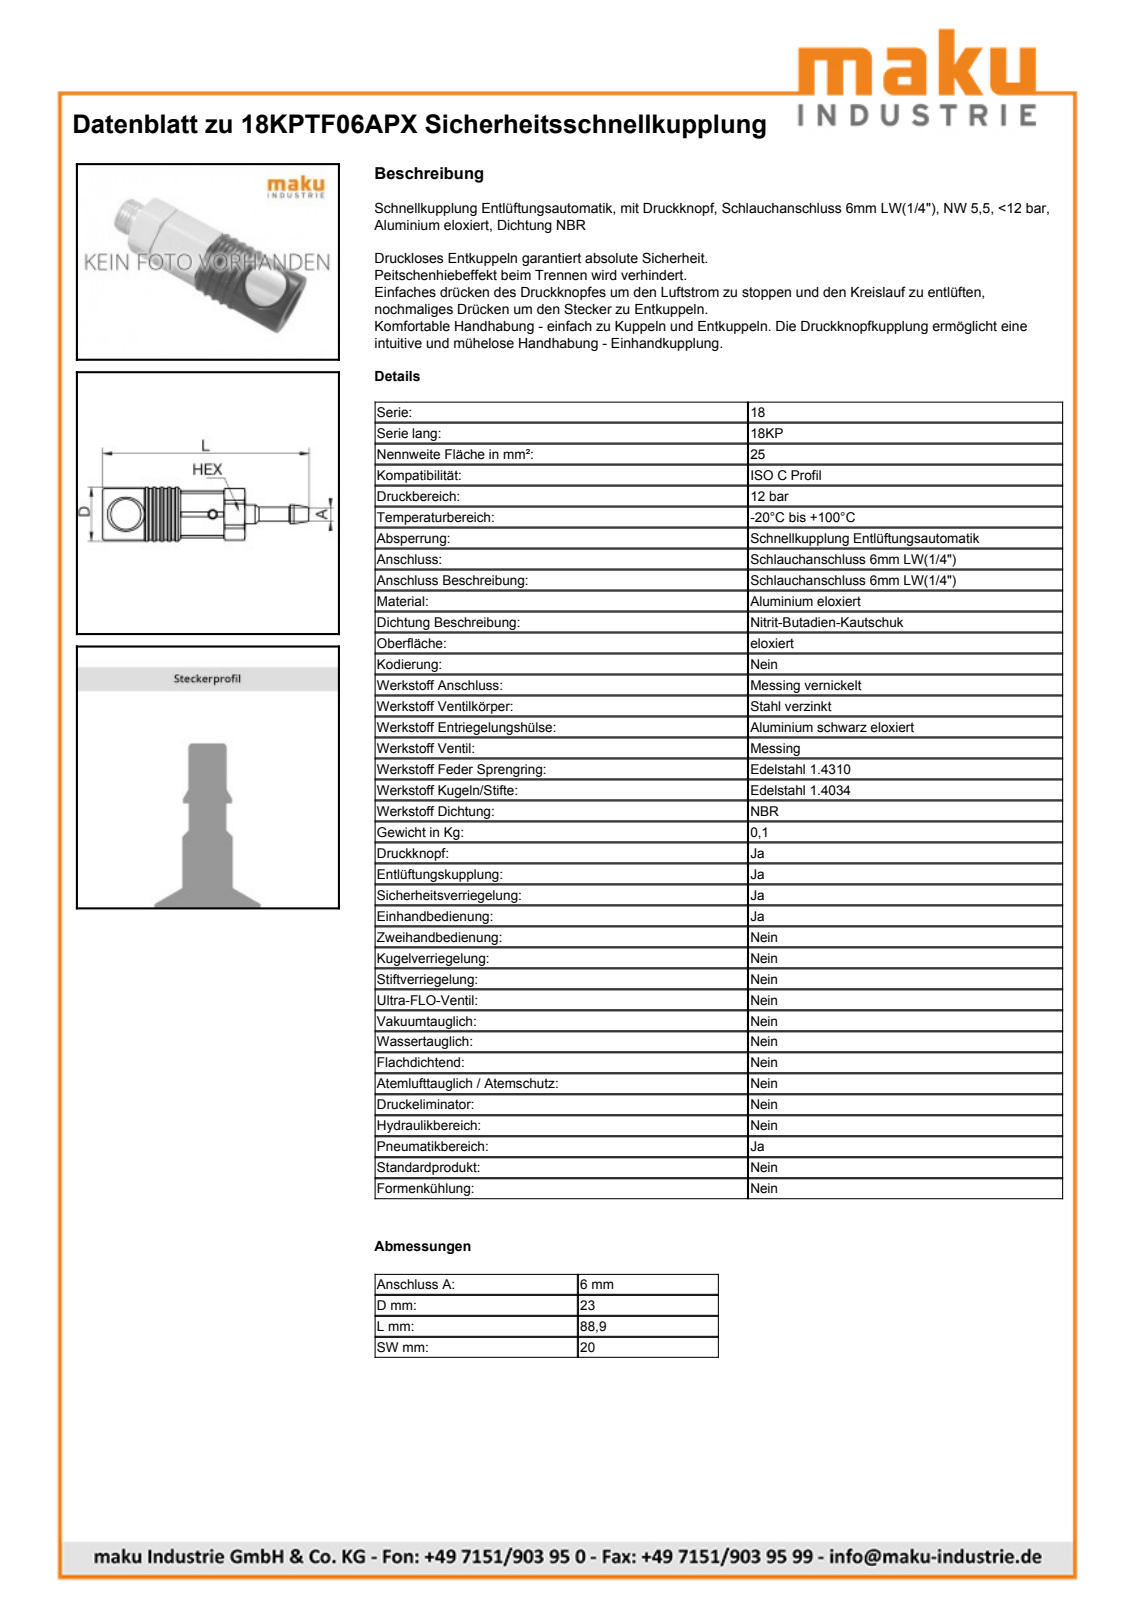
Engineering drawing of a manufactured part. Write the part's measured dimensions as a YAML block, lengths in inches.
part_name: "18KPTF06APX"
step_written_by: "Autodesk Inventor 2019 (CONFIG_CONTROL_DESIGN)"
units: inches
bodies: {solids: 27, faces: 300, planar: 95, cylindrical: 103, other: 102}
overall_size: [3.5, 0.906, 0.906]
volume: 1.88
surface_area: 30.55
round_holes:
  - {diameter: 0.098, count: 1}
  - {diameter: 0.138, count: 1}
  - {diameter: 0.157, count: 1}
  - {diameter: 0.217, count: 1}
  - {diameter: 0.276, count: 1}
  - {diameter: 0.335, count: 1}
  - {diameter: 0.398, count: 1}
  - {diameter: 0.409, count: 1}
  - {diameter: 0.413, count: 1}
  - {diameter: 0.437, count: 1}
  - {diameter: 0.508, count: 1}
  - {diameter: 0.553, count: 1}
round_bosses_or_shafts:
  - {diameter: 0.906, count: 1}
  - {diameter: 0.866, count: 1}
  - {diameter: 0.787, count: 1}
  - {diameter: 0.728, count: 1}
  - {diameter: 0.717, count: 1}
  - {diameter: 0.709, count: 1}
  - {diameter: 0.69, count: 1}
  - {diameter: 0.622, count: 1}
partial_cylinders:
  - {radius: 0.148, count: 1}
  - {radius: 0.284, count: 1}
  - {radius: 0.307, count: 1}
  - {radius: 0.433, count: 1}
  - {radius: 0.487, count: 1}
face_to_face_distances: [0.787, 0.748, 1.157, 1.669, 2.063, 0.906, 0.433, 0.354, 0.177, 1.512]
hole_center_spacings: [0.047, 0.049, 1.474]
